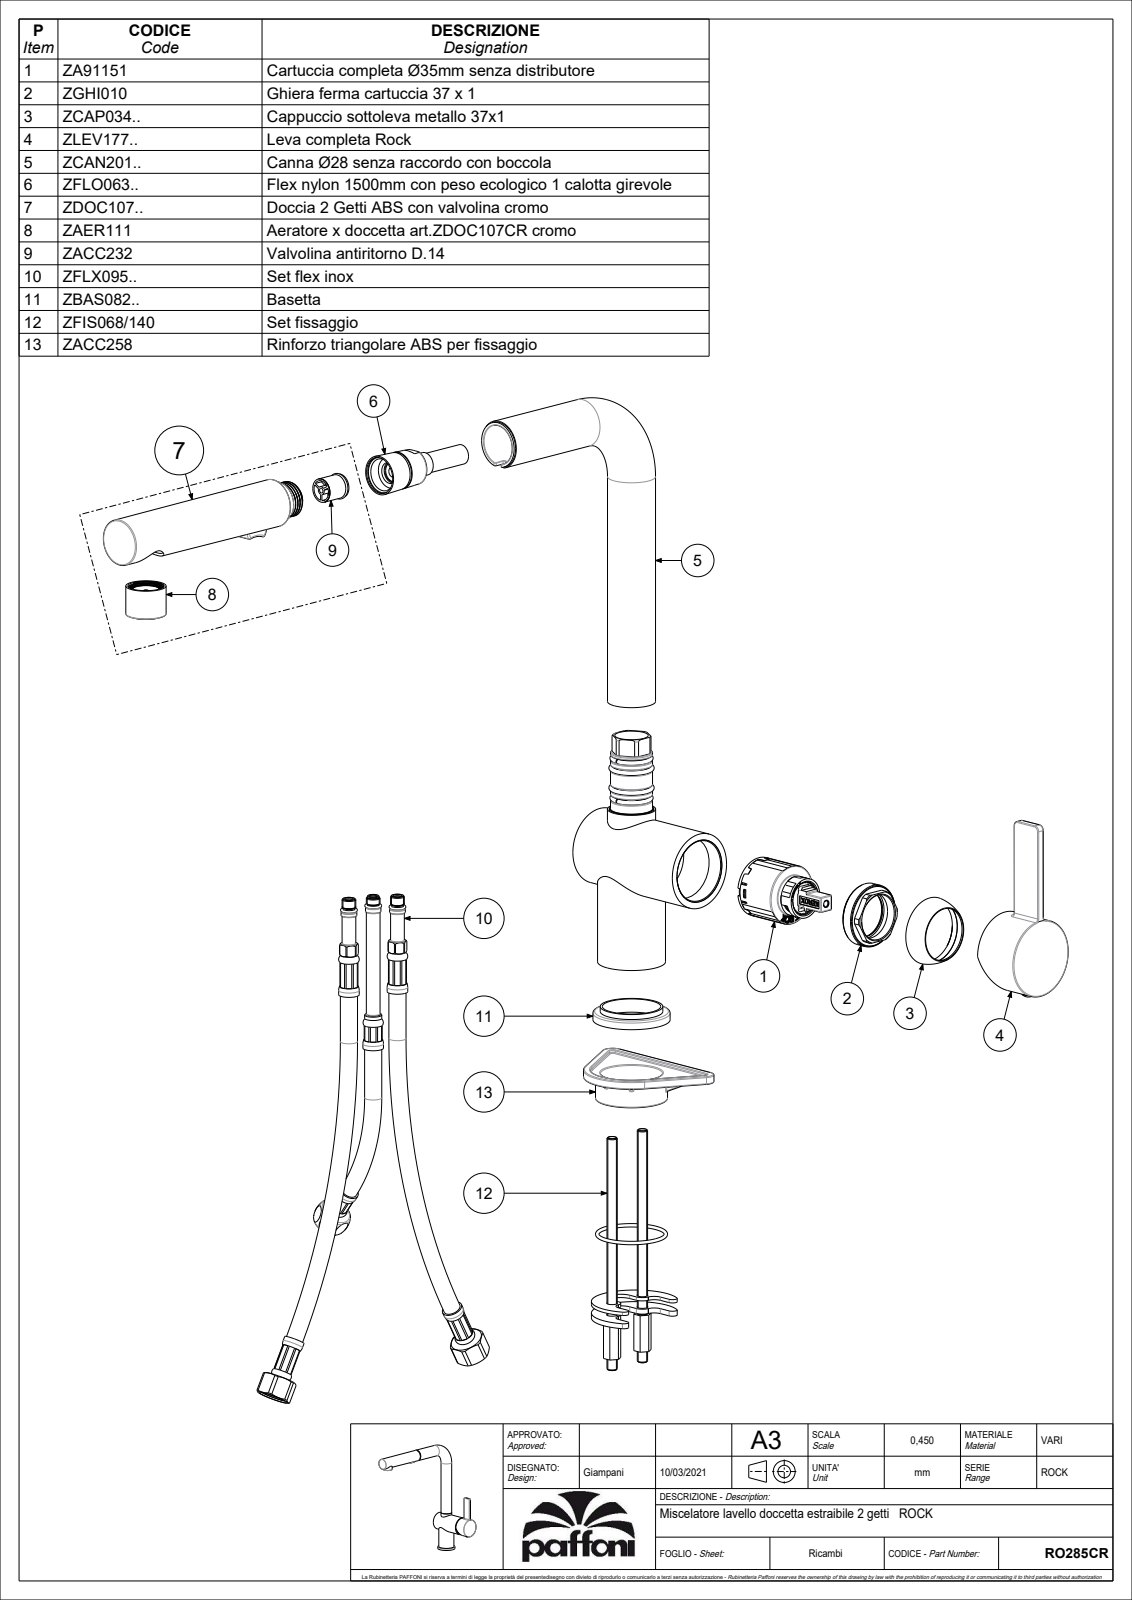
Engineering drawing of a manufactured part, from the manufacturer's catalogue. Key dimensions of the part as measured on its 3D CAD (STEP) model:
Part name (STEP PRODUCT): RO285CR
STEP written by: CREO PARAMETRIC BY PTC INC, 2020044 (CONFIG_CONTROL_DESIGN)
Units: millimetres
Bodies: 0 solids, 125 faces (31 planar, 48 cylindrical, 46 other)
Overall size (bounding box): 286.7 × 260.75 × 114.1
Round holes (diameter × count): ⌀25 ×1
Round bosses / shafts (diameter × count): ⌀28 ×2, ⌀45.5 ×1, ⌀45 ×1, ⌀44.7 ×1, ⌀39.6 ×1, ⌀26.8 ×1, ⌀22.8 ×1, ⌀21 ×1
Partial cylindrical surfaces — rounded edges, fillets, slot ends (radius × count): R0.5 ×6, R1 ×3, R2 ×2, R3 ×2, R9 ×2, R1.95 ×1, R12.2 ×1, R17 ×1
Main face-to-face distances: 82, 5, 4.5, 240.25, 235.75, 105.75, 101.25, 134.5, 107.06, 102.56
